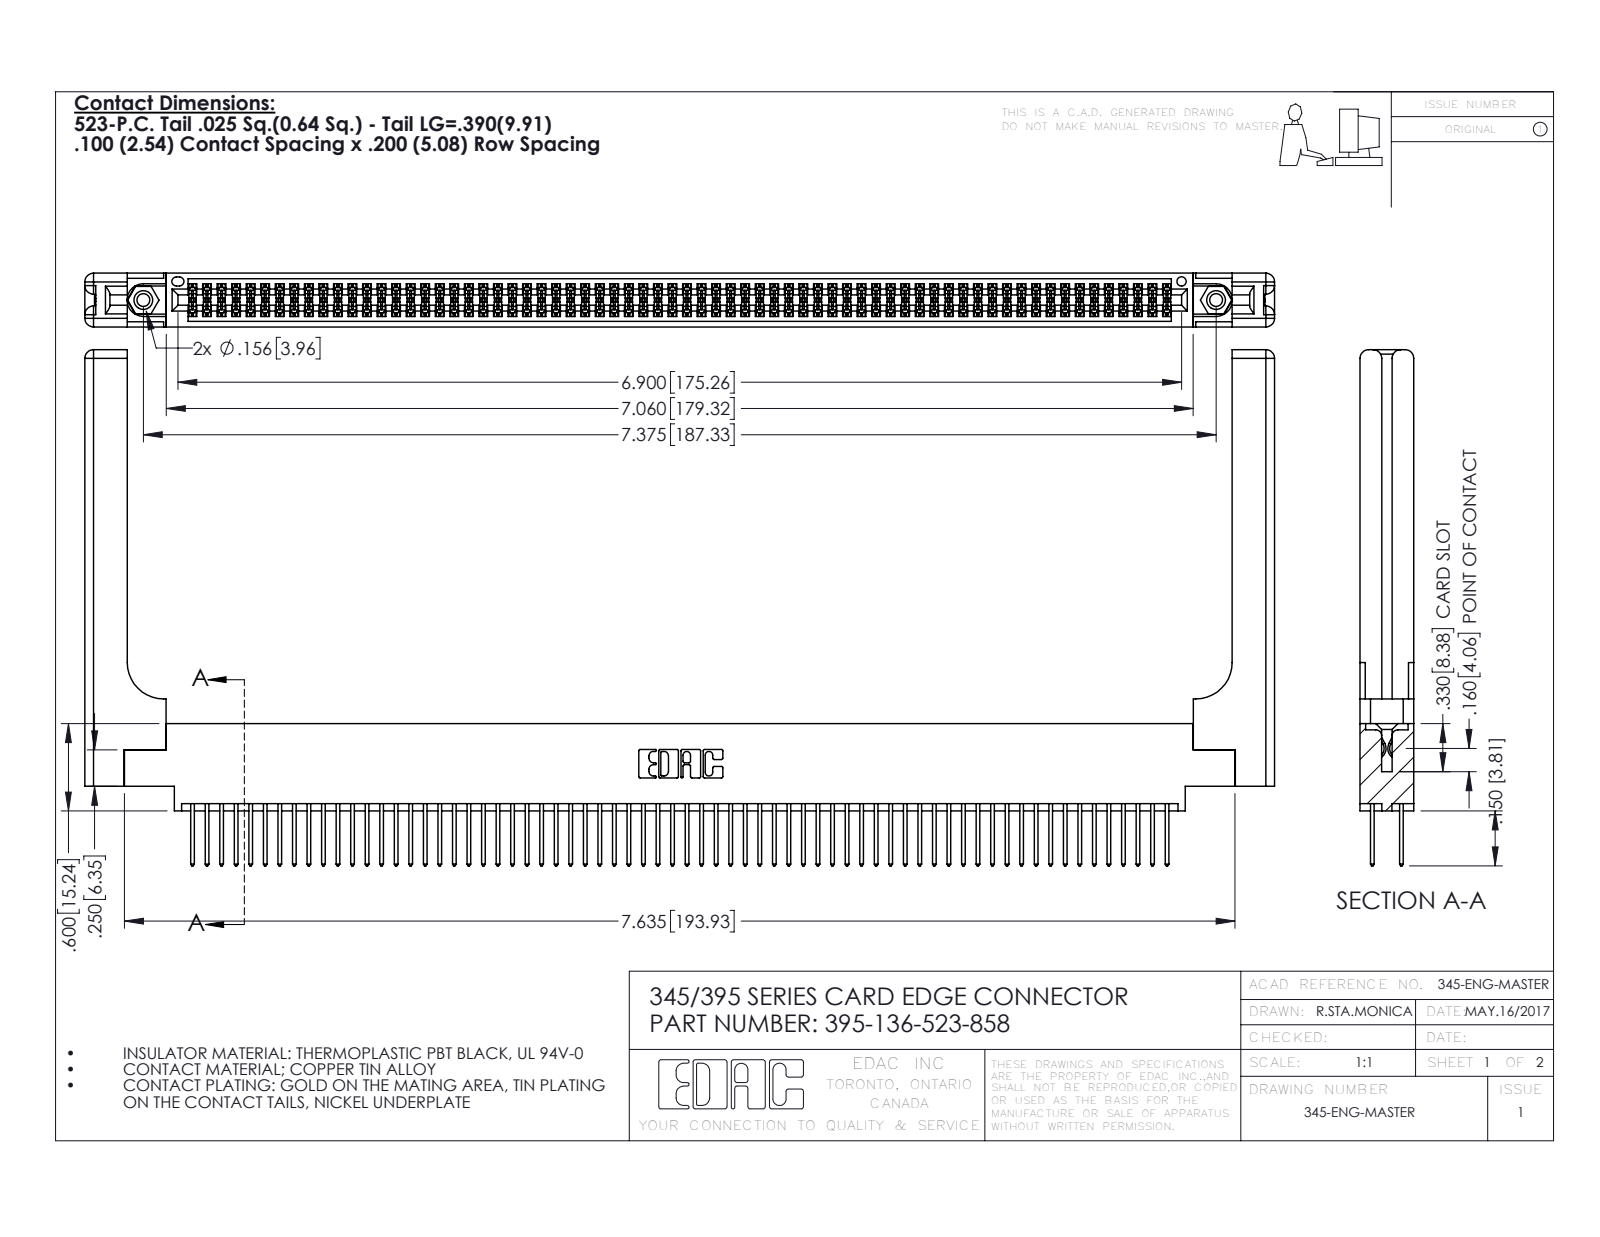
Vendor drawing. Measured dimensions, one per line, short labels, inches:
name: 345-220-058_345-220-058; 345-292-001_345-293-123; 345-250-001_345-250-001-102; 395-136-523-858 (+1 more)
written by: SolidWorks 2016 (CONFIG_CONTROL_DESIGN)
unit: in
bodies: 141 solids, 7186 faces (4720 planar, 2406 cylindrical, 60 other)
size: 8.179 × 3.547 × 0.37
volume: 1.774 in³; area: 57.95 in²
holes: 2× ⌀0.089, 2× ⌀0.125, 2× ⌀0.156, 1× ⌀0.064
bosses: 2× ⌀0.155
rounds: 204× R0.006, 136× R0.01, 22× R0.01, 16× R0.06, 6× R0.007, 6× R0.031, 3× R0.026, 2× R0.014
face distances: 0.072, 0.298, 0.37, 0.098, 0.272, 0.025, 0.2, 0.225, 0.175, 0.148
hole spacings: 0.27, 7.139, 7.375
